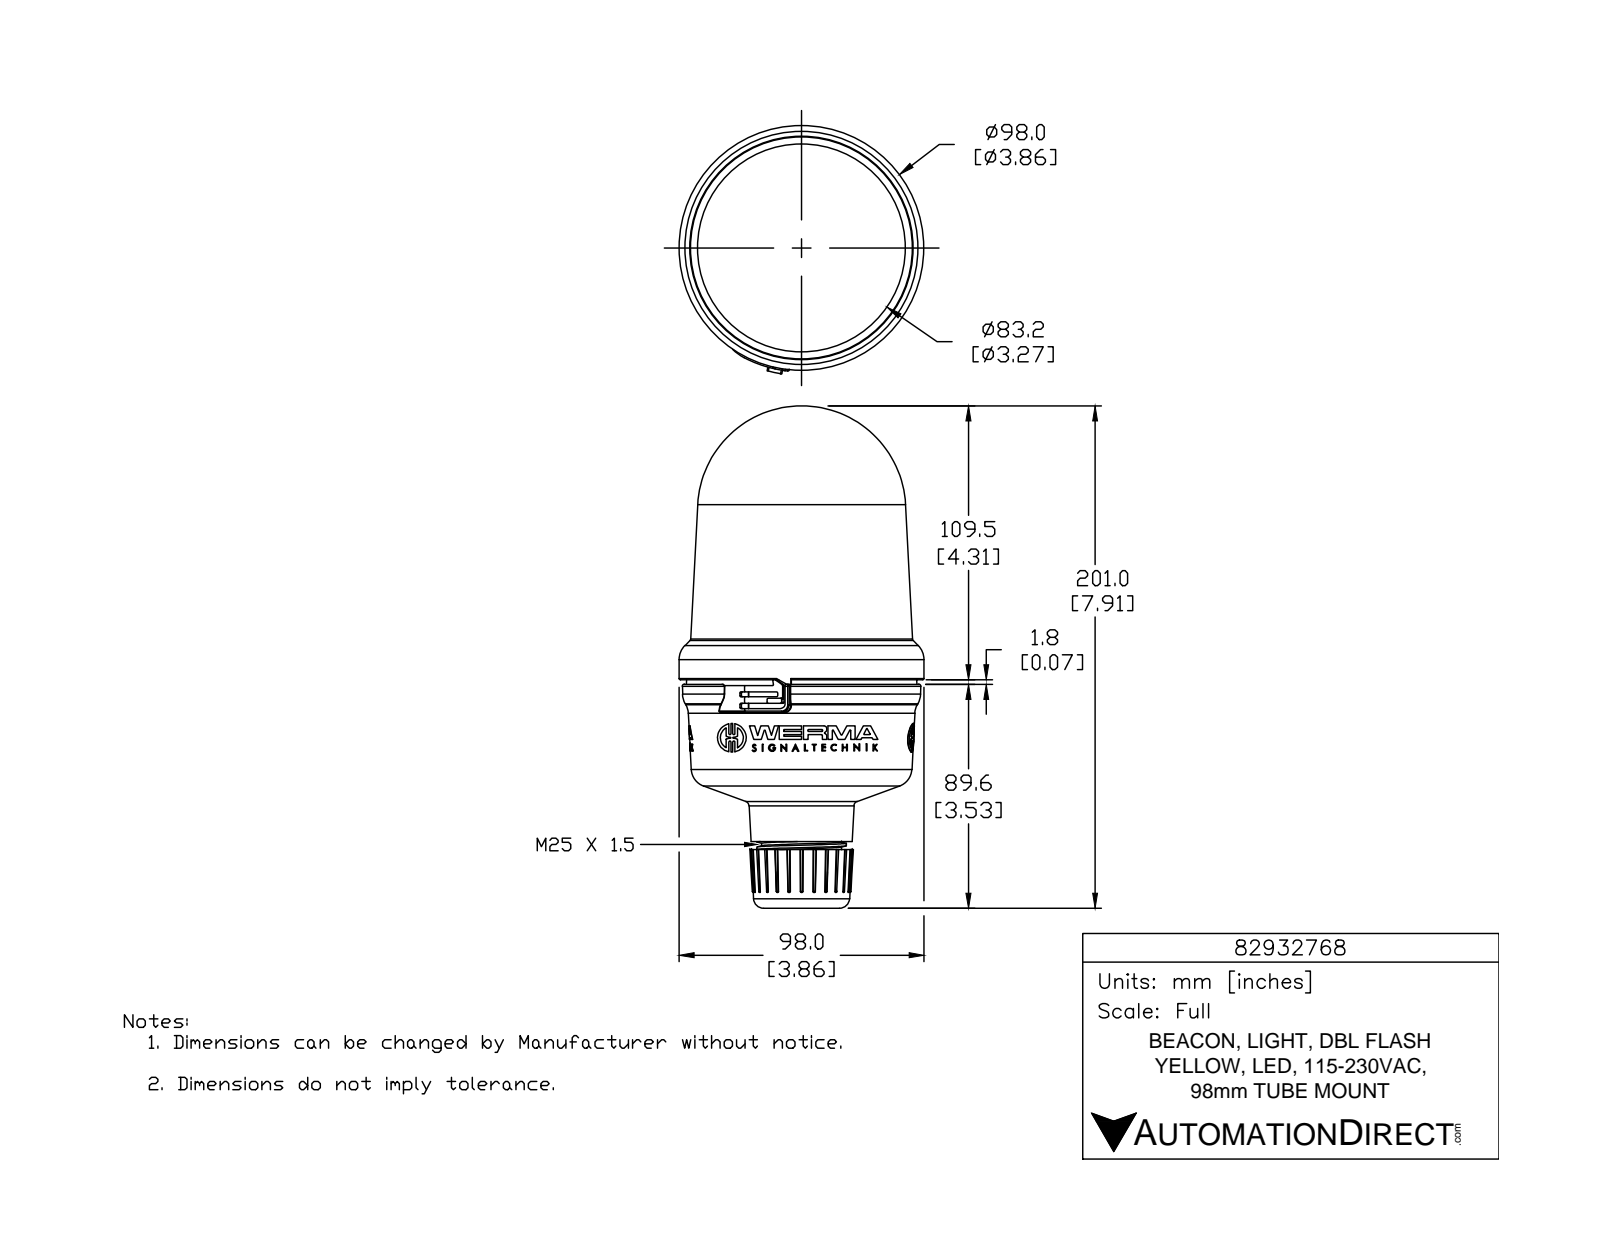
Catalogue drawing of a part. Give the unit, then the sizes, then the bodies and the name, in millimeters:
Units: millimetres
Overall size (bounding box): 201 × 99.4 × 98
Round holes (diameter × count): ⌀2 ×3, ⌀25.7 ×1, ⌀26 ×1
Round bosses / shafts (diameter × count): ⌀11.5 ×3, ⌀2.9 ×3, ⌀98 ×1, ⌀35.8 ×1, ⌀32 ×1
Partial cylindrical surfaces — rounded edges, fillets, slot ends (radius × count): R0.5 ×12, R0.2 ×9, R0.2 ×6, R0.4 ×6, R0.4 ×6, R0.4 ×6, R6.7 ×6, R0.2 ×3
Main face-to-face distances: 56.2, 11.7, 68, 8.5, 3.2, 64.7, 66.1, 62.9, 54.4, 1.9
Volume: 896 400 mm³ · Surface area: 58 960 mm²
Bodies: 1 solid, 1006 faces (554 planar, 189 cylindrical, 263 other)
Part name (STEP PRODUCT): 82932768
STEP written by: SolidWorks 2015 (AUTOMOTIVE_DESIGN)
